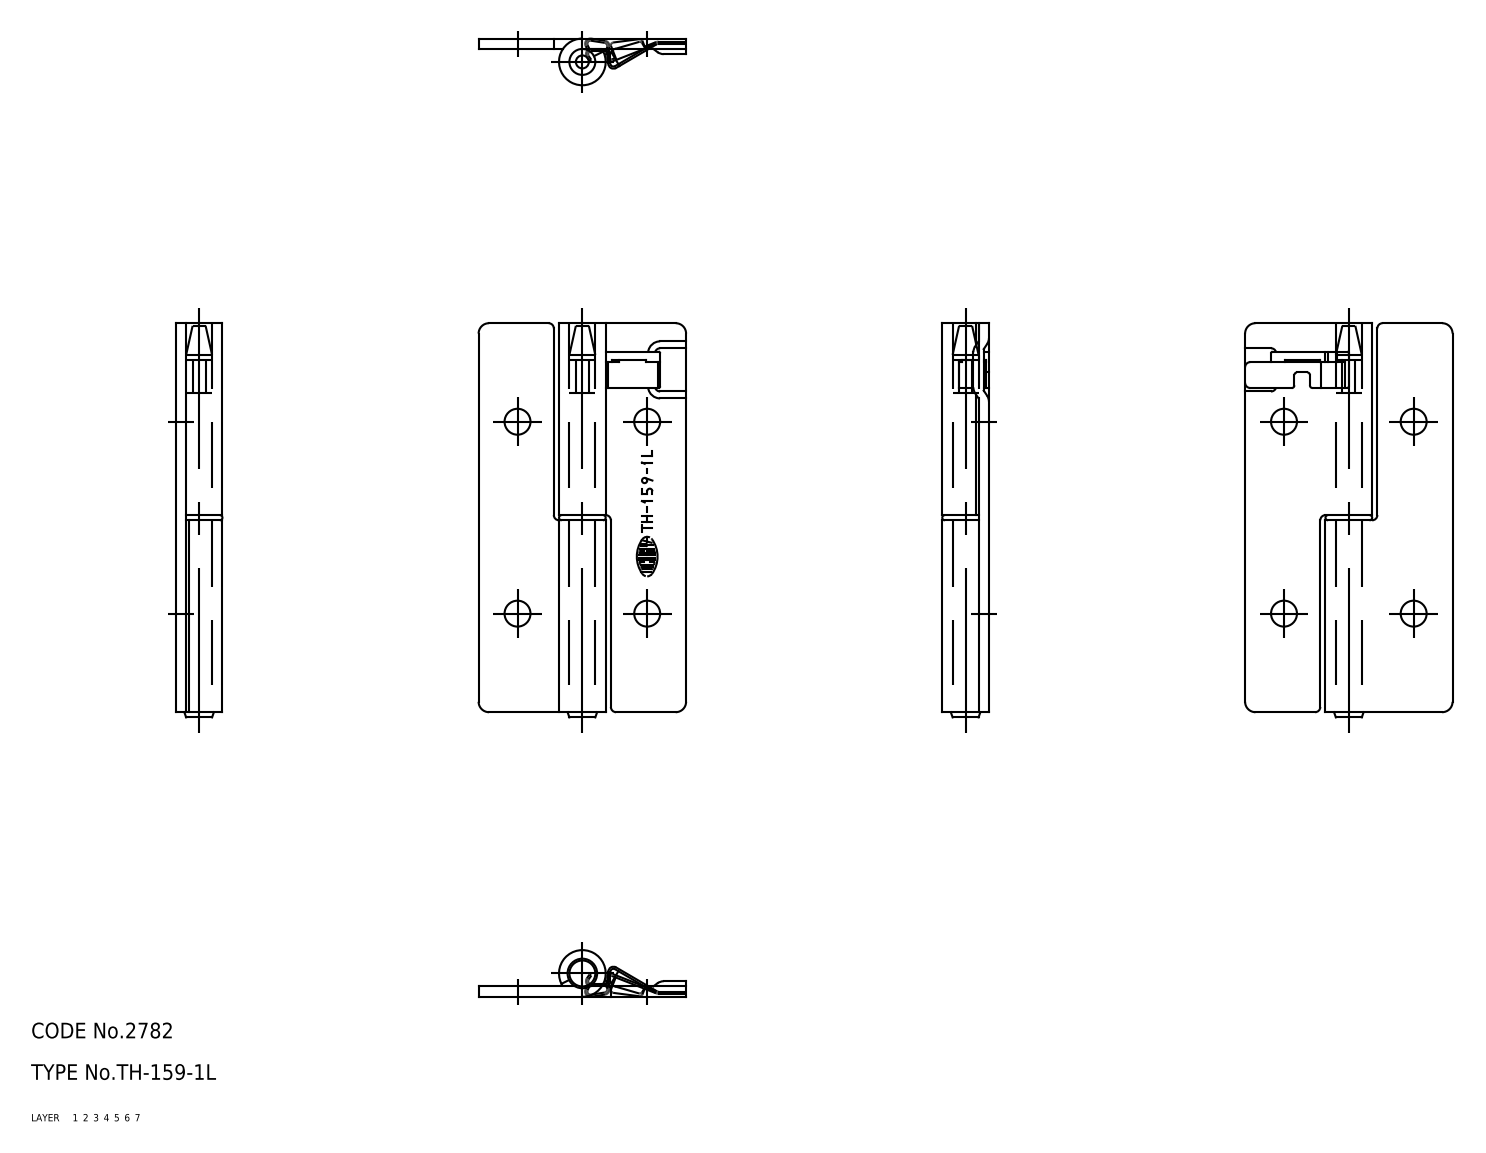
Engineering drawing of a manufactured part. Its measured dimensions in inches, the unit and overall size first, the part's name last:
Units: inches
Overall size (bounding box): 2.992 × 1.575 × 0.354
Volume: 0.545 in³ · Surface area: 15.79 in²
Bodies: 4 solids, 128 faces (0 planar, 0 cylindrical, 128 other)
Part name (STEP PRODUCT): 67115288; 67115301; 67115314; 67115327
STEP written by: CADfix (AUTOMOTIVE_DESIGN)
